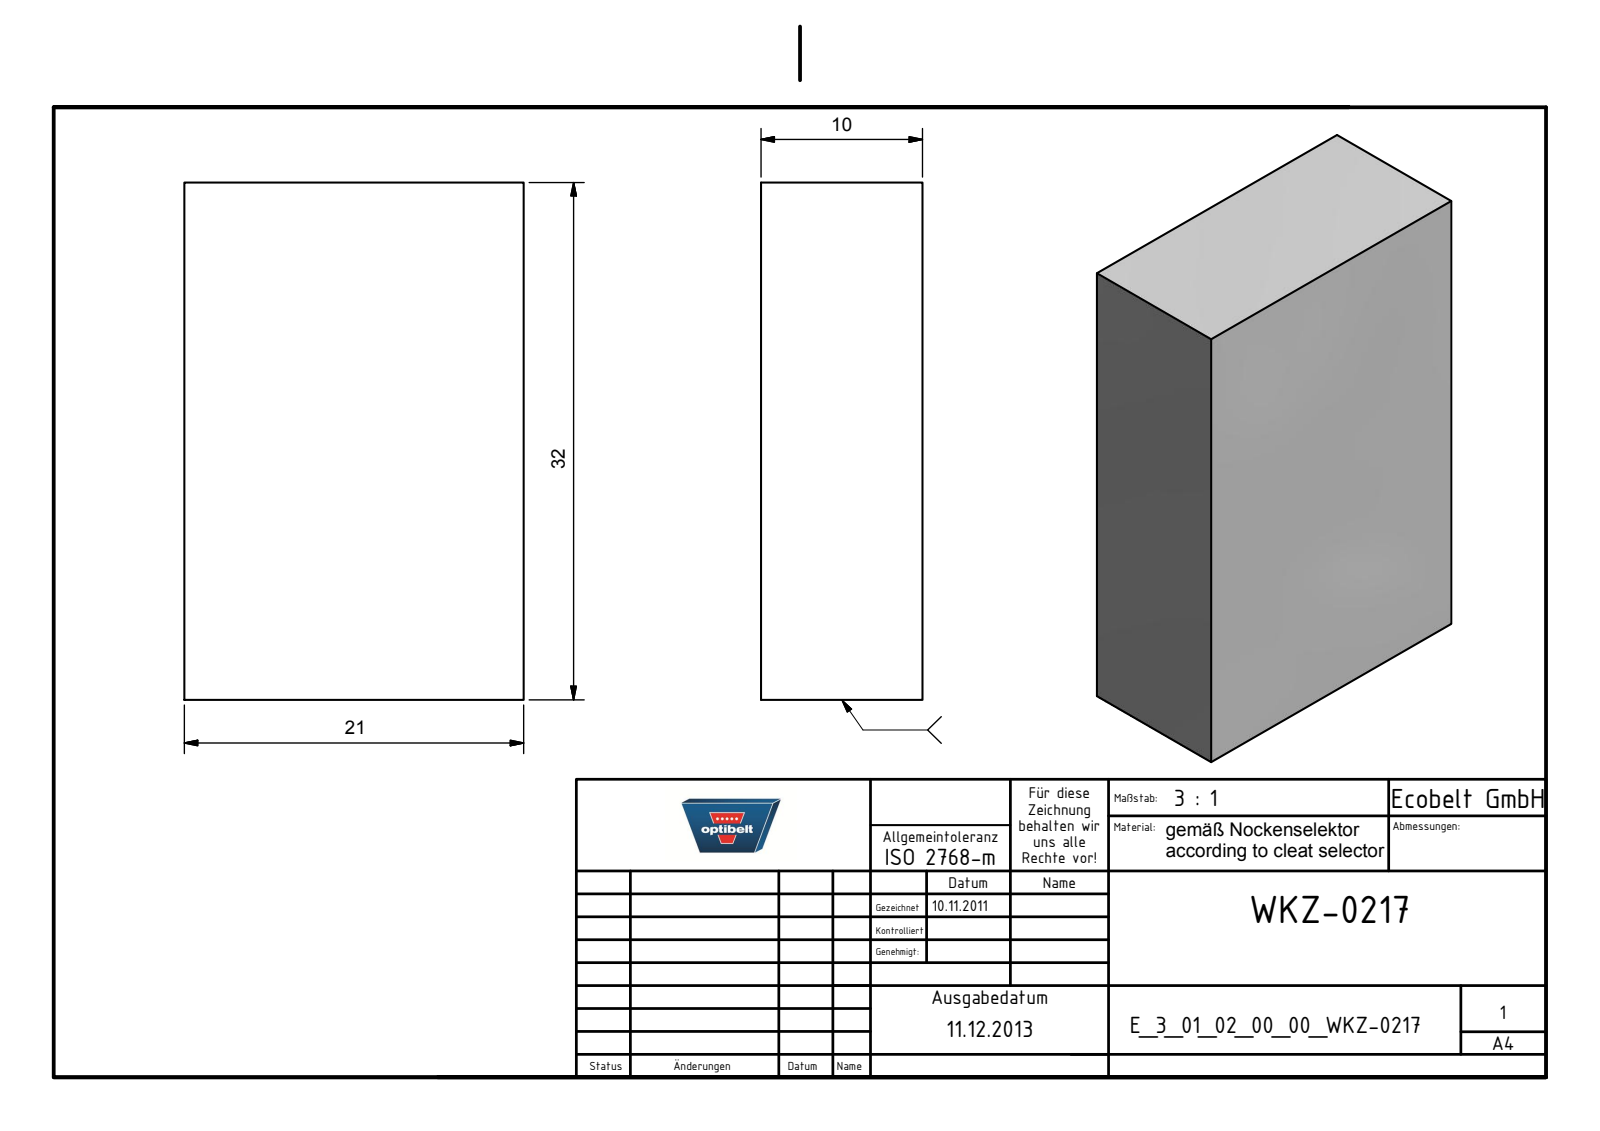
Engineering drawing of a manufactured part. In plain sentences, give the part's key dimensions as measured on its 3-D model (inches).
The part is named "E_3_01_02_00_00_WKZ-0217". Its 3-D file was written by "Autodesk Inventor 2021 (AUTOMOTIVE_DESIGN)". It is 1 solid with 6 faces: 6 planar, 0 cylindrical and 0 other. Overall it measures 1.26 by 0.827 by 0.394 inches. Its volume is 0.41 cubic inches and its surface area 3.726 square inches. The main face-to-face distances are 0.394, 0.827, 1.26.
